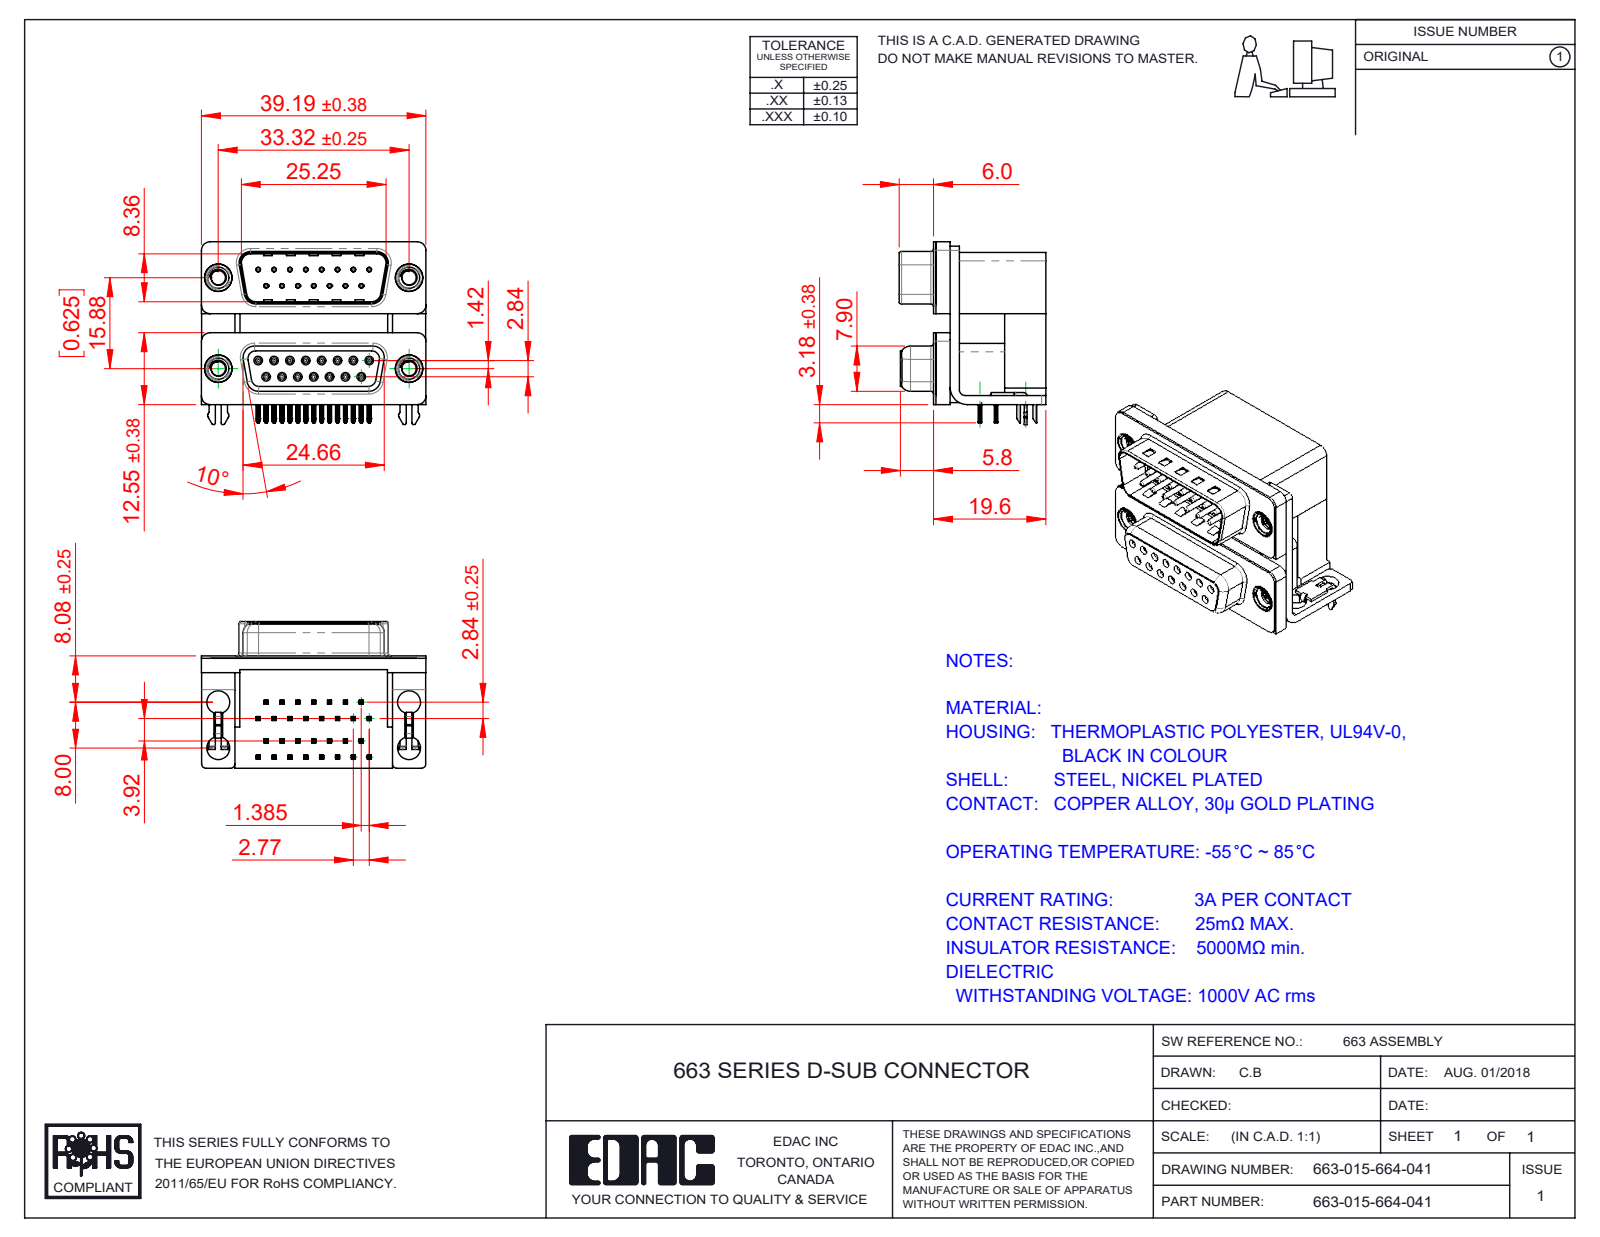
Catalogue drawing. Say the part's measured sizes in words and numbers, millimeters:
The part is named "663 Contact Top Upper_L; 663 Housing Lower_15 Contacts; 663 Housing Upper_15 Contacts L; 663 Shell Receptacle_15 Contacts (+8 more)". Its 3-D file was written by "SolidWorks 2020 (CONFIG_CONTROL_DESIGN)". It is 43 solids with 4024 faces: 2093 planar, 1052 cylindrical and 879 other. Overall it measures 39.19 by 31.93 by 25.6 millimeters. Its volume is 14 573 cubic millimeters and its surface area 16 323 square millimeters. Round holes: 30 of diameter 0.8, 15 of diameter 0.35, 15 of diameter 0.9, 8 of diameter 4, 4 of diameter 2.5, 4 of diameter 3.5, 4 of diameter 4.8, 4 of diameter 5. Round bosses or shafts: 15 of diameter 1.2, 15 of diameter 0.75, 4 of diameter 4.9, 4 of diameter 4.75, 4 of diameter 3.9. Partial cylindrical surfaces (rounded edges, fillets, slot ends): 121 of radius 0.1, 66 of radius 0.25, 60 of radius 0.15, 30 of radius 0.12, 30 of radius 0.35, 16 of radius 0.5, 16 of radius 1.5, 15 of radius 0.34. The main face-to-face distances are 0.4, 19.2, 16.7, 2.5, 10.7, 7.2, 12, 9.5, 2.9, 19.6. The hole center spacings are 3.16, 16.12, 2.77, 16.82, 5.54, 8.31, 15.88, 17.92.
